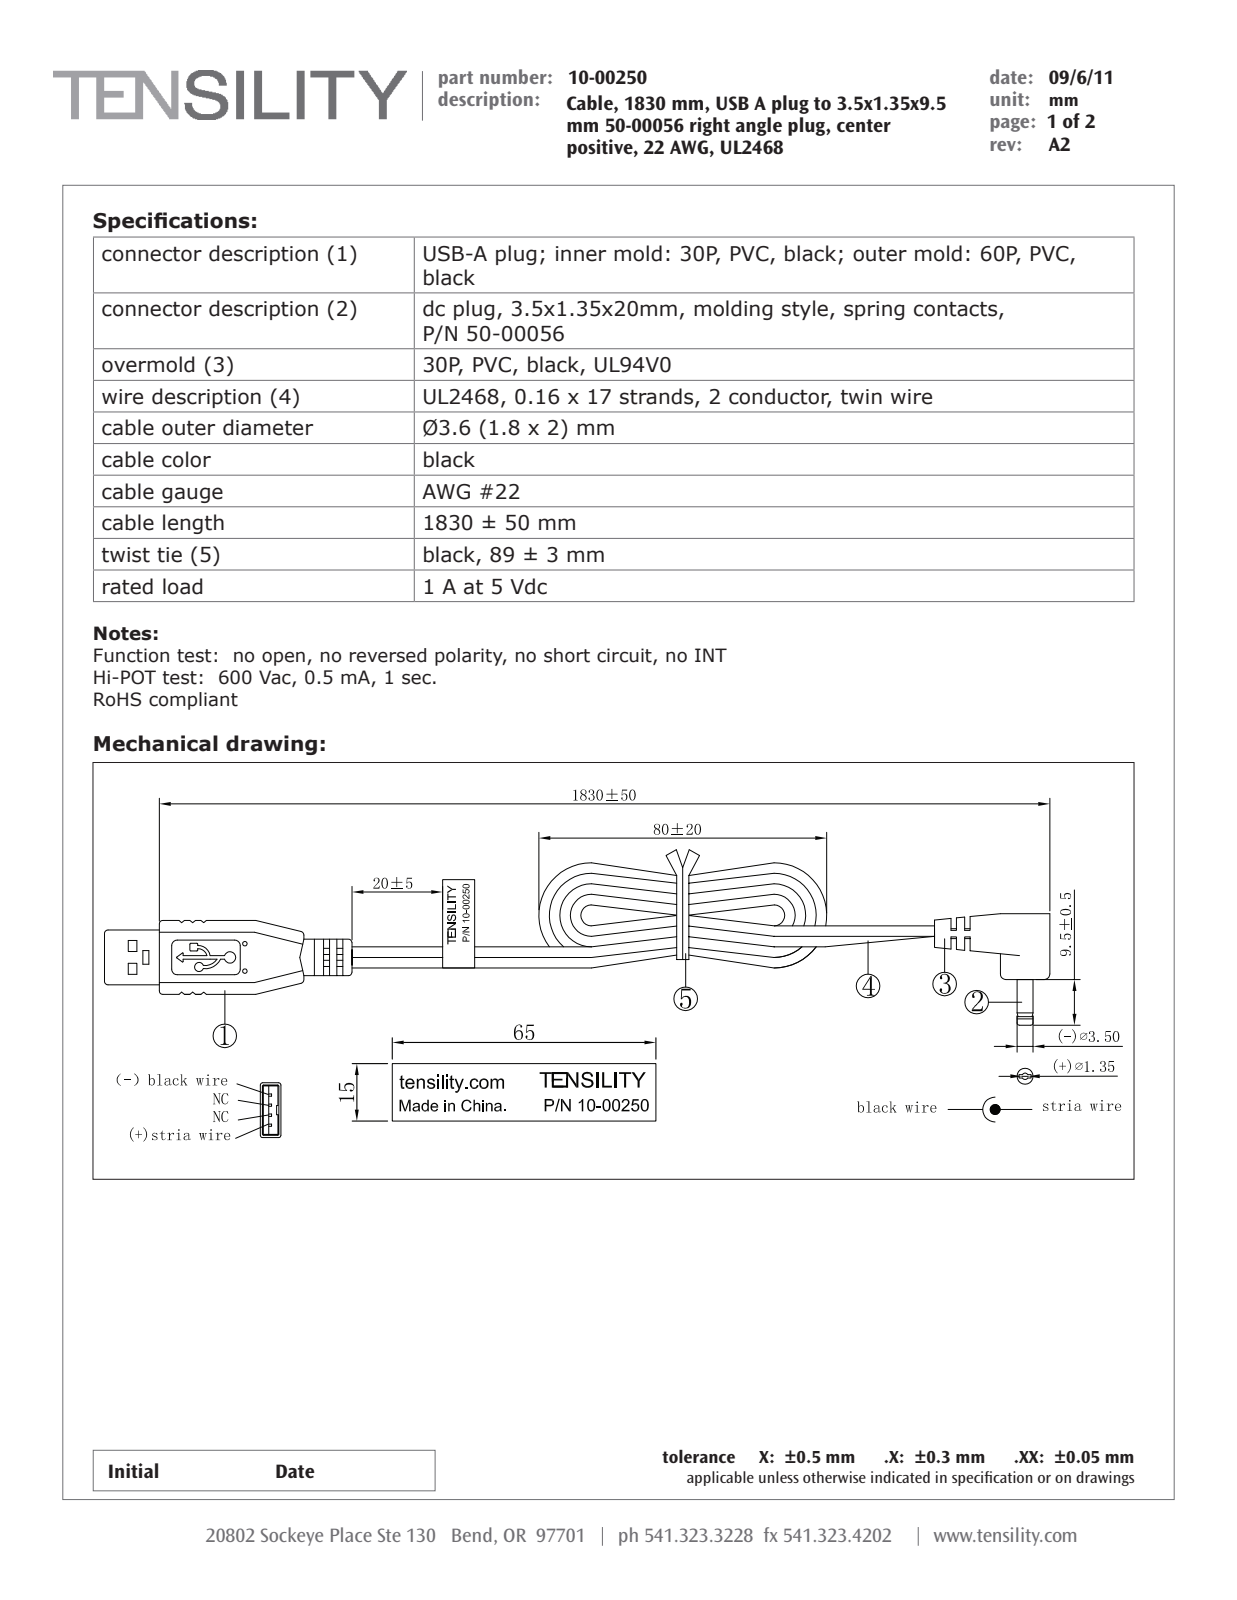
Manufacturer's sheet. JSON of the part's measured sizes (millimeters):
{"part_name": "50-00056; 30-00008_wbc; 10-00250_revA3; 24-00023 (+8 more)", "step_written_by": "SolidWorks 2015 (AUTOMOTIVE_DESIGN)", "units": "millimeters", "bodies": {"solids": 62, "faces": 1214, "planar": 605, "cylindrical": 327, "other": 282}, "overall_size": [212.1, 48.5, 8.75], "volume_mm3": 7739, "surface_area_mm2": 13249, "round_holes": [[0.85, 2], [1.2, 1], [1.35, 1], [1.5, 1], [1.8, 1], [2.9, 1], [3.5, 1], [3.8, 1]], "round_bosses_or_shafts": [[4, 2], [1.9, 2], [8.75, 1], [8, 1], [7.26, 1], [4.5, 1], [4.2, 1], [3.82, 1]], "partial_cylinders_radius": [[0.1, 68], [0.5, 11], [0.15, 10], [0.2, 8], [0.75, 8], [0.3, 4], [0.64, 4], [1.3, 4]], "face_to_face_distances": [1.95, 1.86, 1.81, 2.01, 6.45, 2.33, 3.87, 2.06, 4.5, 4.28], "hole_center_spacings": [1.78]}
